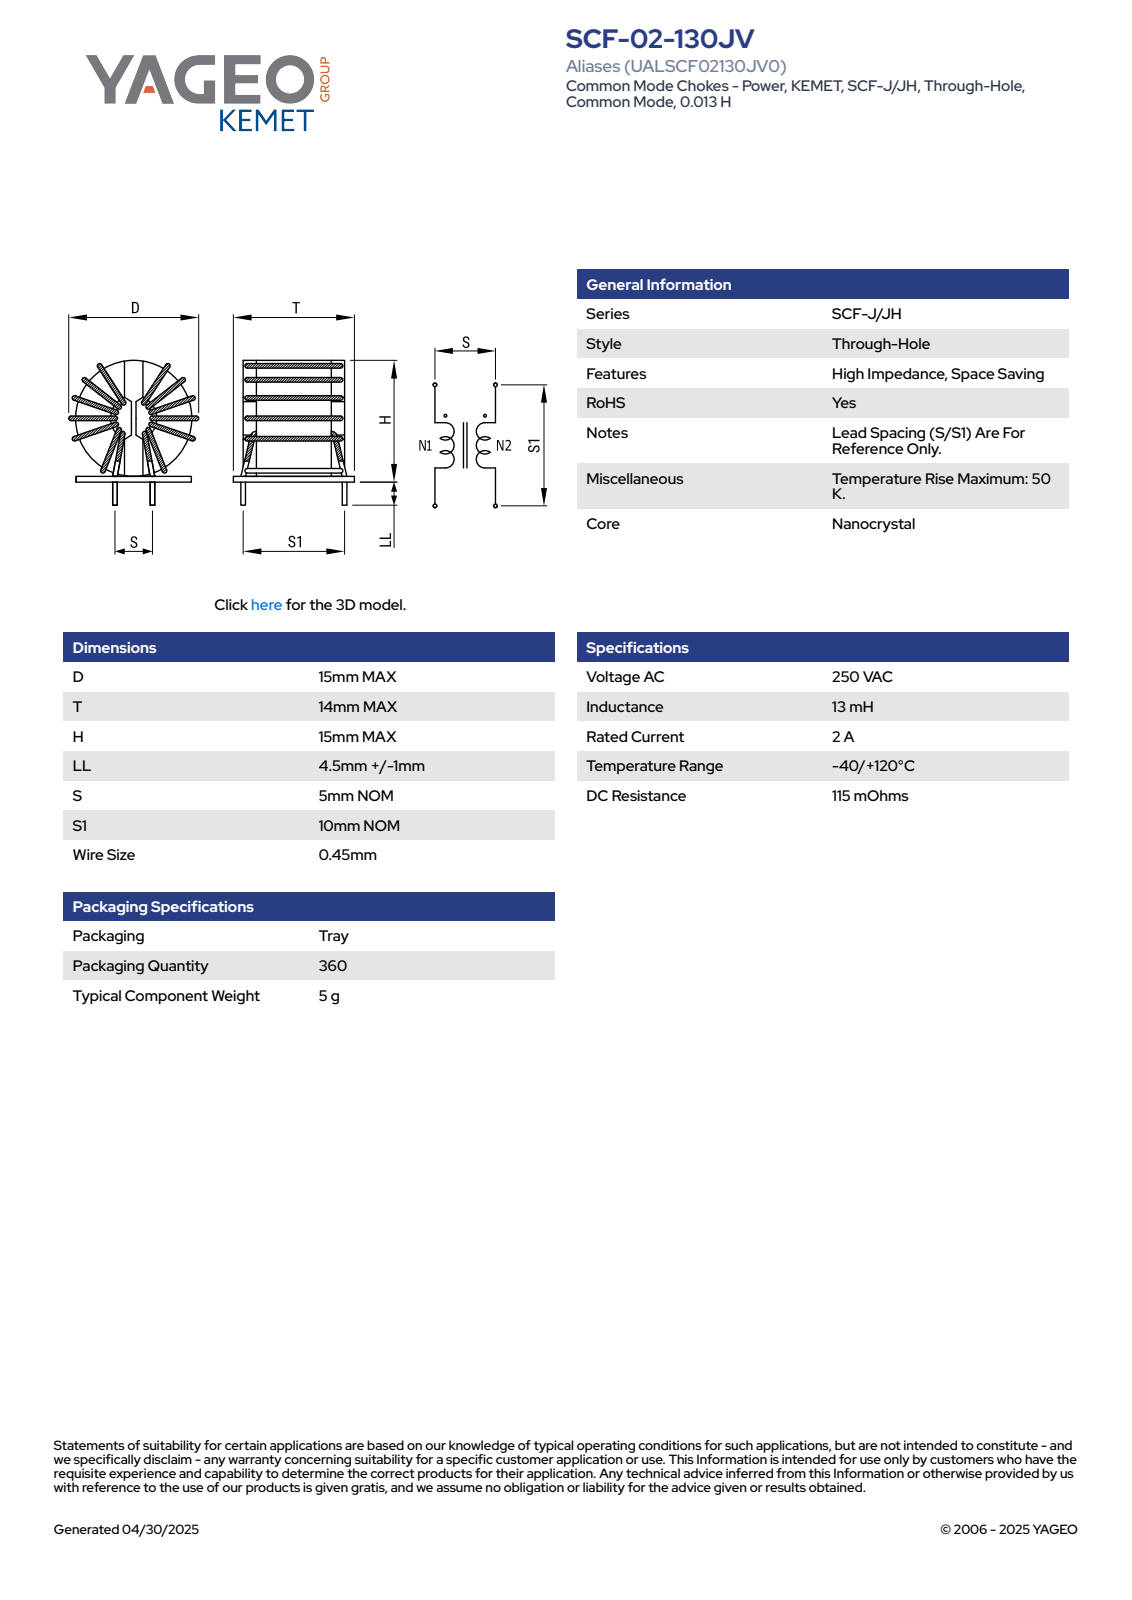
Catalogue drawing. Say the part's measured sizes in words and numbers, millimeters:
The part is named "SCF-02-130JV". Its 3-D file was written by "SolidWorks 2018 (AUTOMOTIVE_DESIGN)". It is 1 solid with 227 faces: 91 planar, 74 cylindrical and 62 other. Overall it measures 19.5 by 15 by 14 millimeters. Its volume is 1 852 cubic millimeters and its surface area 1 666 square millimeters. Round holes: 4 of diameter 0.6. Round bosses or shafts: 8 of diameter 0.45. Partial cylindrical surfaces (rounded edges, fillets, slot ends): 16 of radius 0.23, 2 of radius 1.3, 1 of radius 2, 1 of radius 2.9, 1 of radius 6.8, 1 of radius 6.8, 1 of radius 7.5. The main face-to-face distances are 1, 10.8, 1.8, 0.8, 1.6, 12.4, 2.6, 6.2, 7, 8. The hole center spacings are 5, 10, 11.18.
